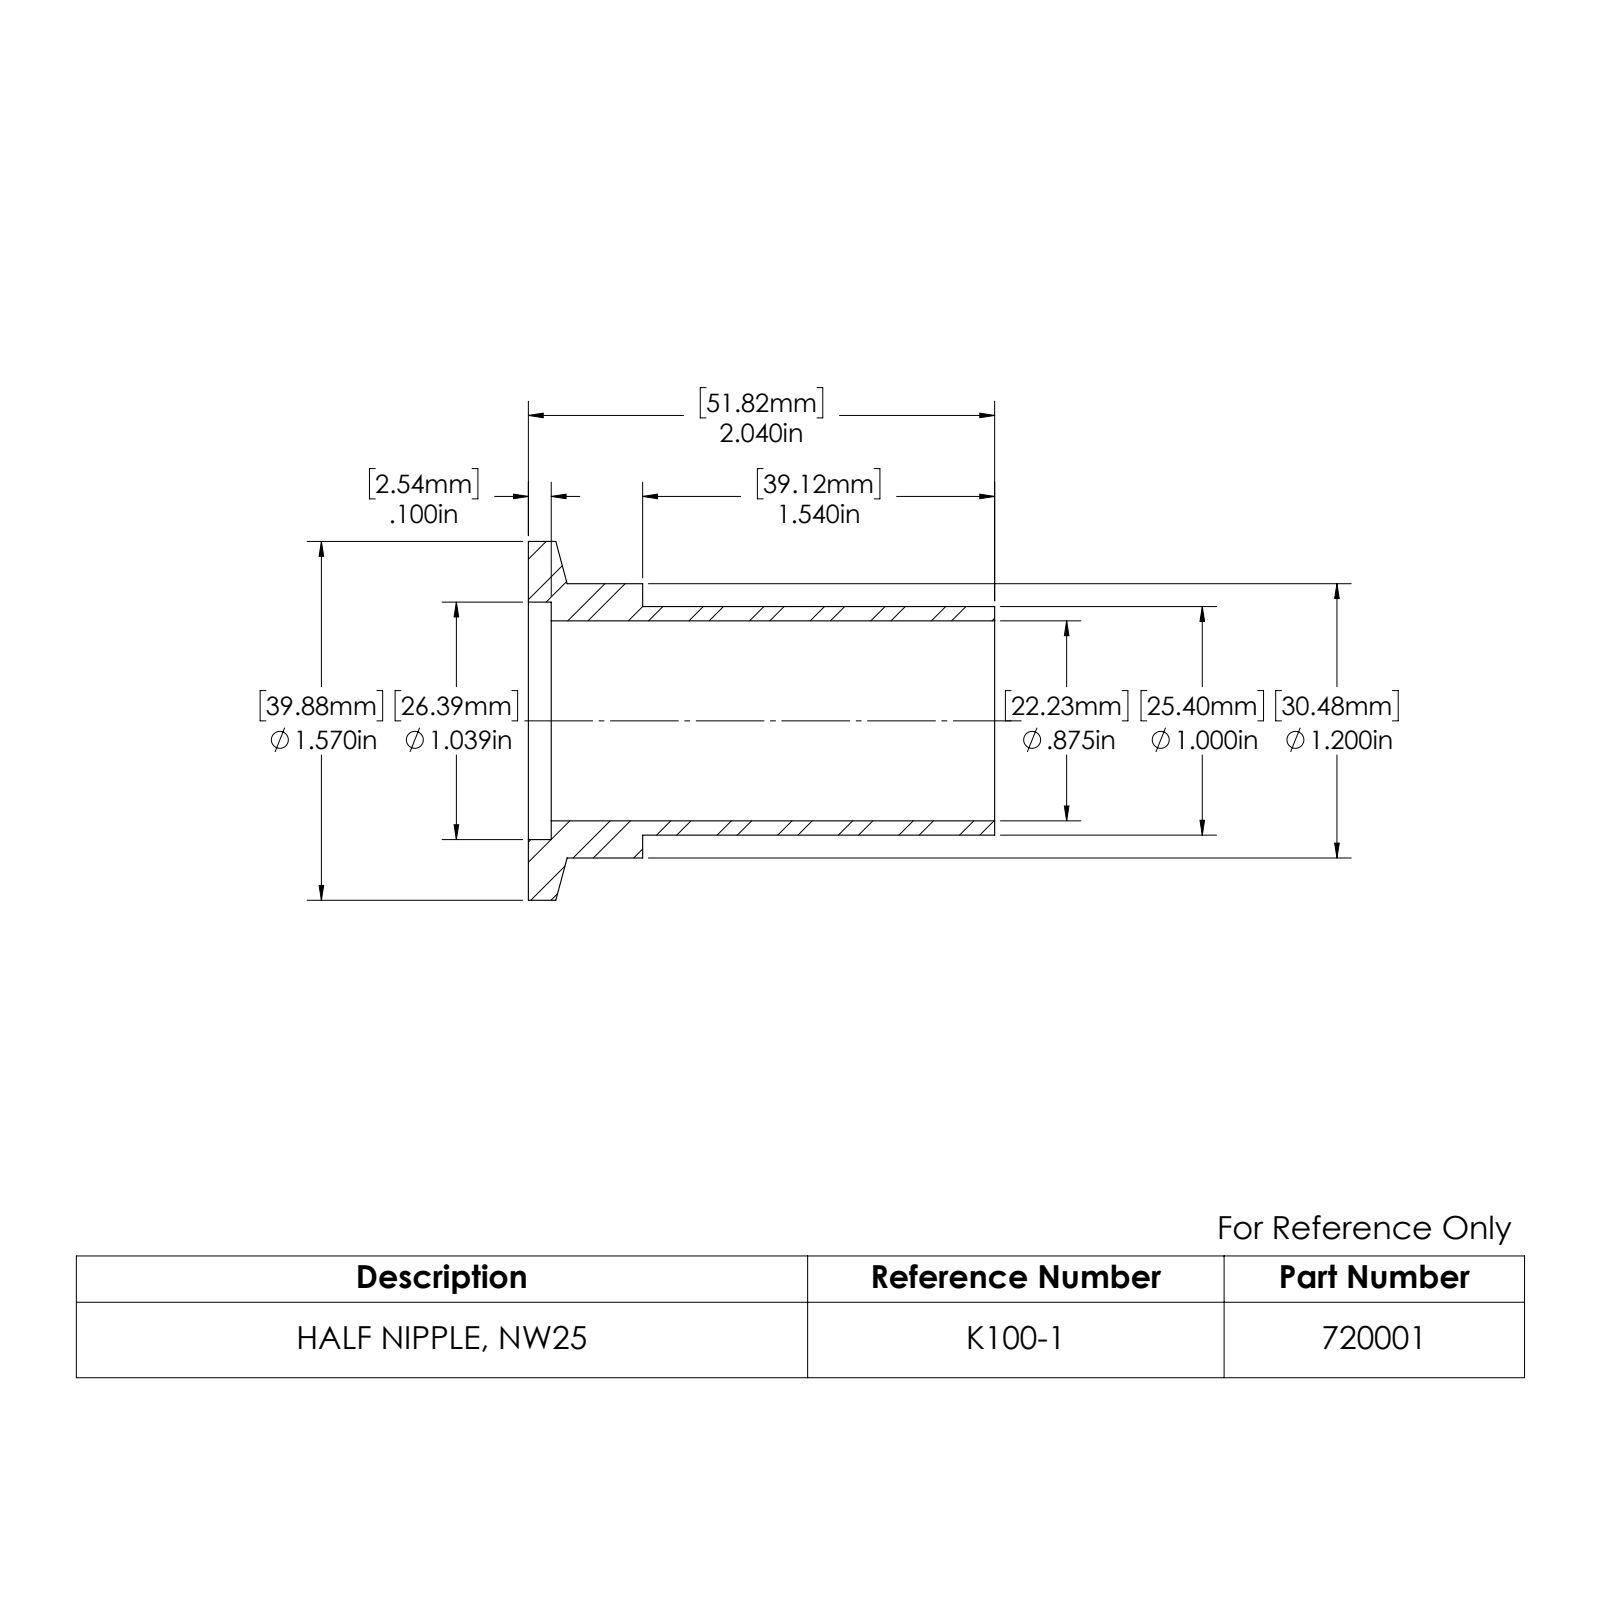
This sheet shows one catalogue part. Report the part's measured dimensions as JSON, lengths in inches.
{"part_name": "720001", "step_written_by": "SolidWorks 2022 (AUTOMOTIVE_DESIGN)", "units": "inches", "bodies": {"solids": 1, "faces": 16, "planar": 4, "cylindrical": 10, "other": 2}, "overall_size": [2.04, 1.57, 1.57], "volume_in3": 0.639, "surface_area_in2": 15.03, "round_holes": [[0.875, 1], [1.039, 1]], "round_bosses_or_shafts": [[1.57, 1], [1.2, 1], [1, 1]], "face_to_face_distances": [0.5, 0.1, 0.4, 2.04, 1.94, 1.54]}
